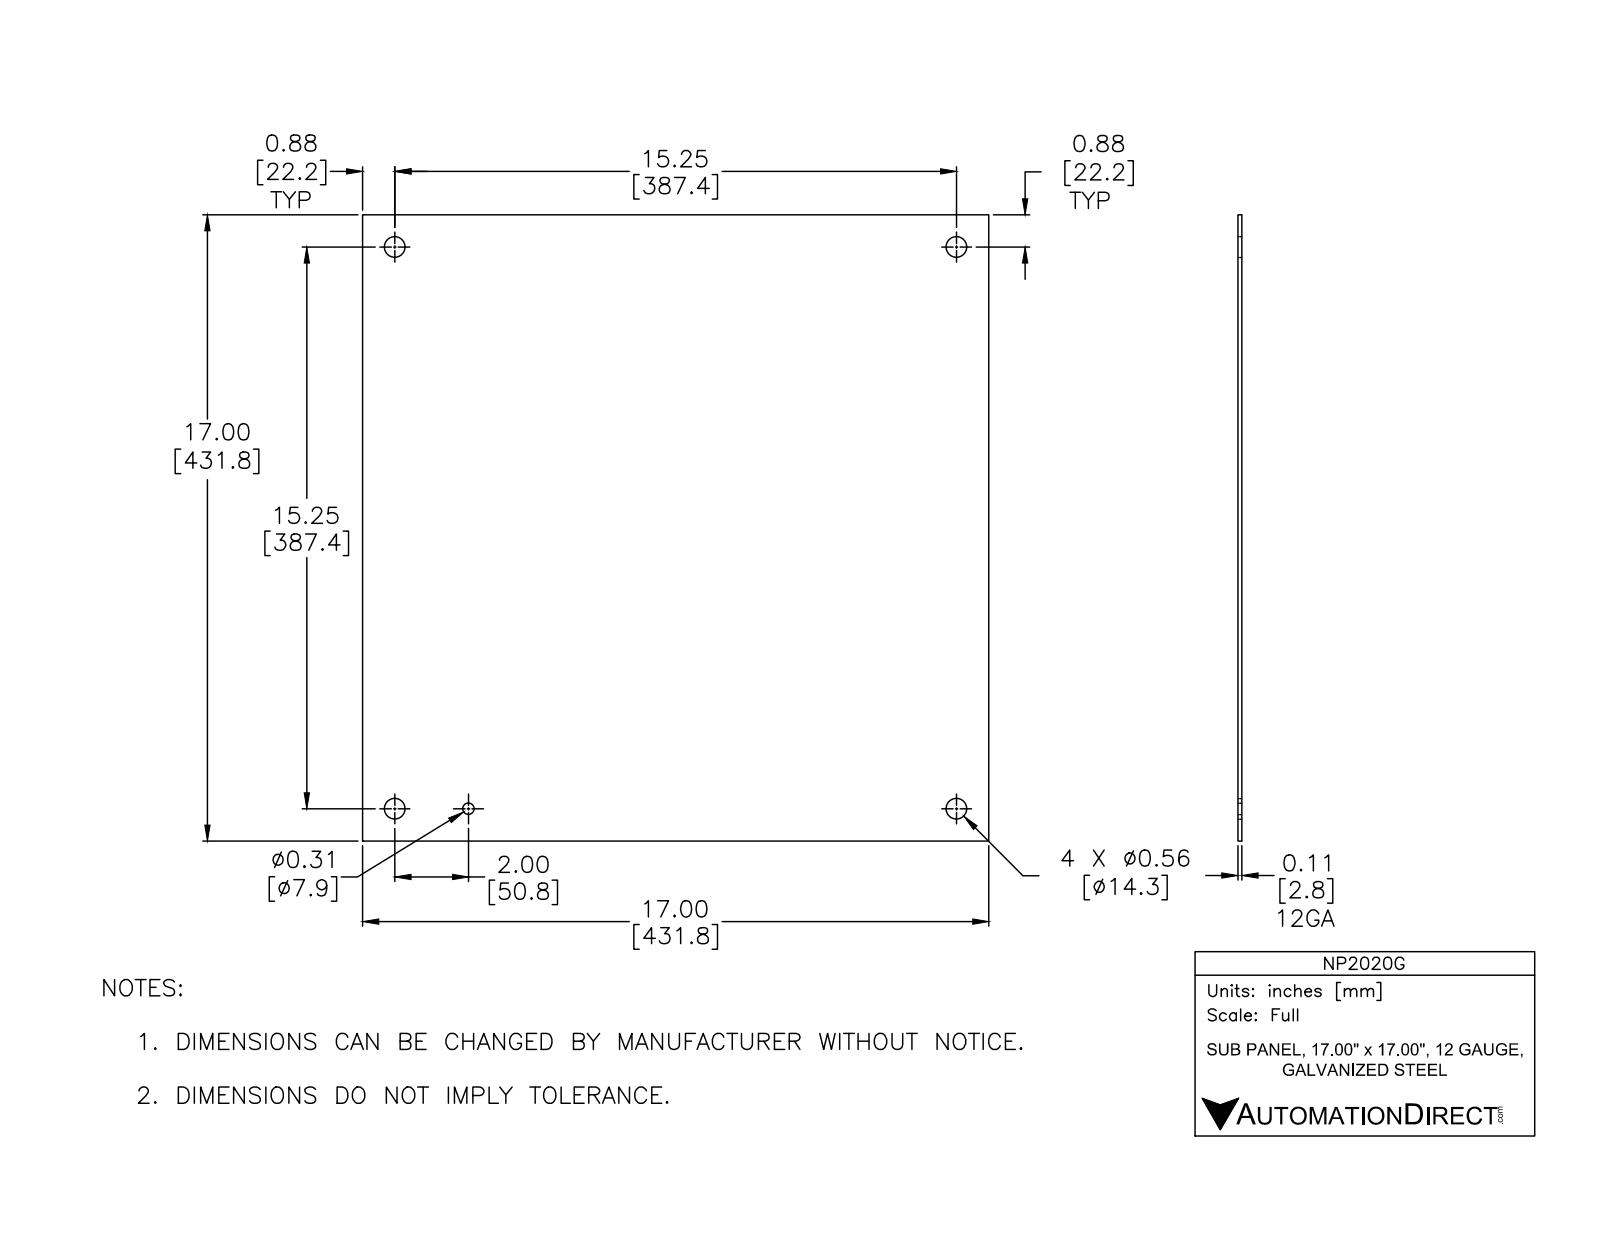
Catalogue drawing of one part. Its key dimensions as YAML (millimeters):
part_name: "NP2020G"
step_written_by: "Autodesk Inventor 2012 (AUTOMOTIVE_DESIGN)"
units: millimeters
bodies: {solids: 1, faces: 11, planar: 6, cylindrical: 5, other: 0}
overall_size: [431.8, 431.8, 2.4]
volume: 442100
surface_area: 376100
round_holes:
  - {diameter: 14.3, count: 4}
  - {diameter: 7.9, count: 1}
face_to_face_distances: [2.4, 431.8]
hole_center_spacings: [387.4, 50.8, 336.6, 387.4, 390.7, 513.1, 547.8, 547.8]
